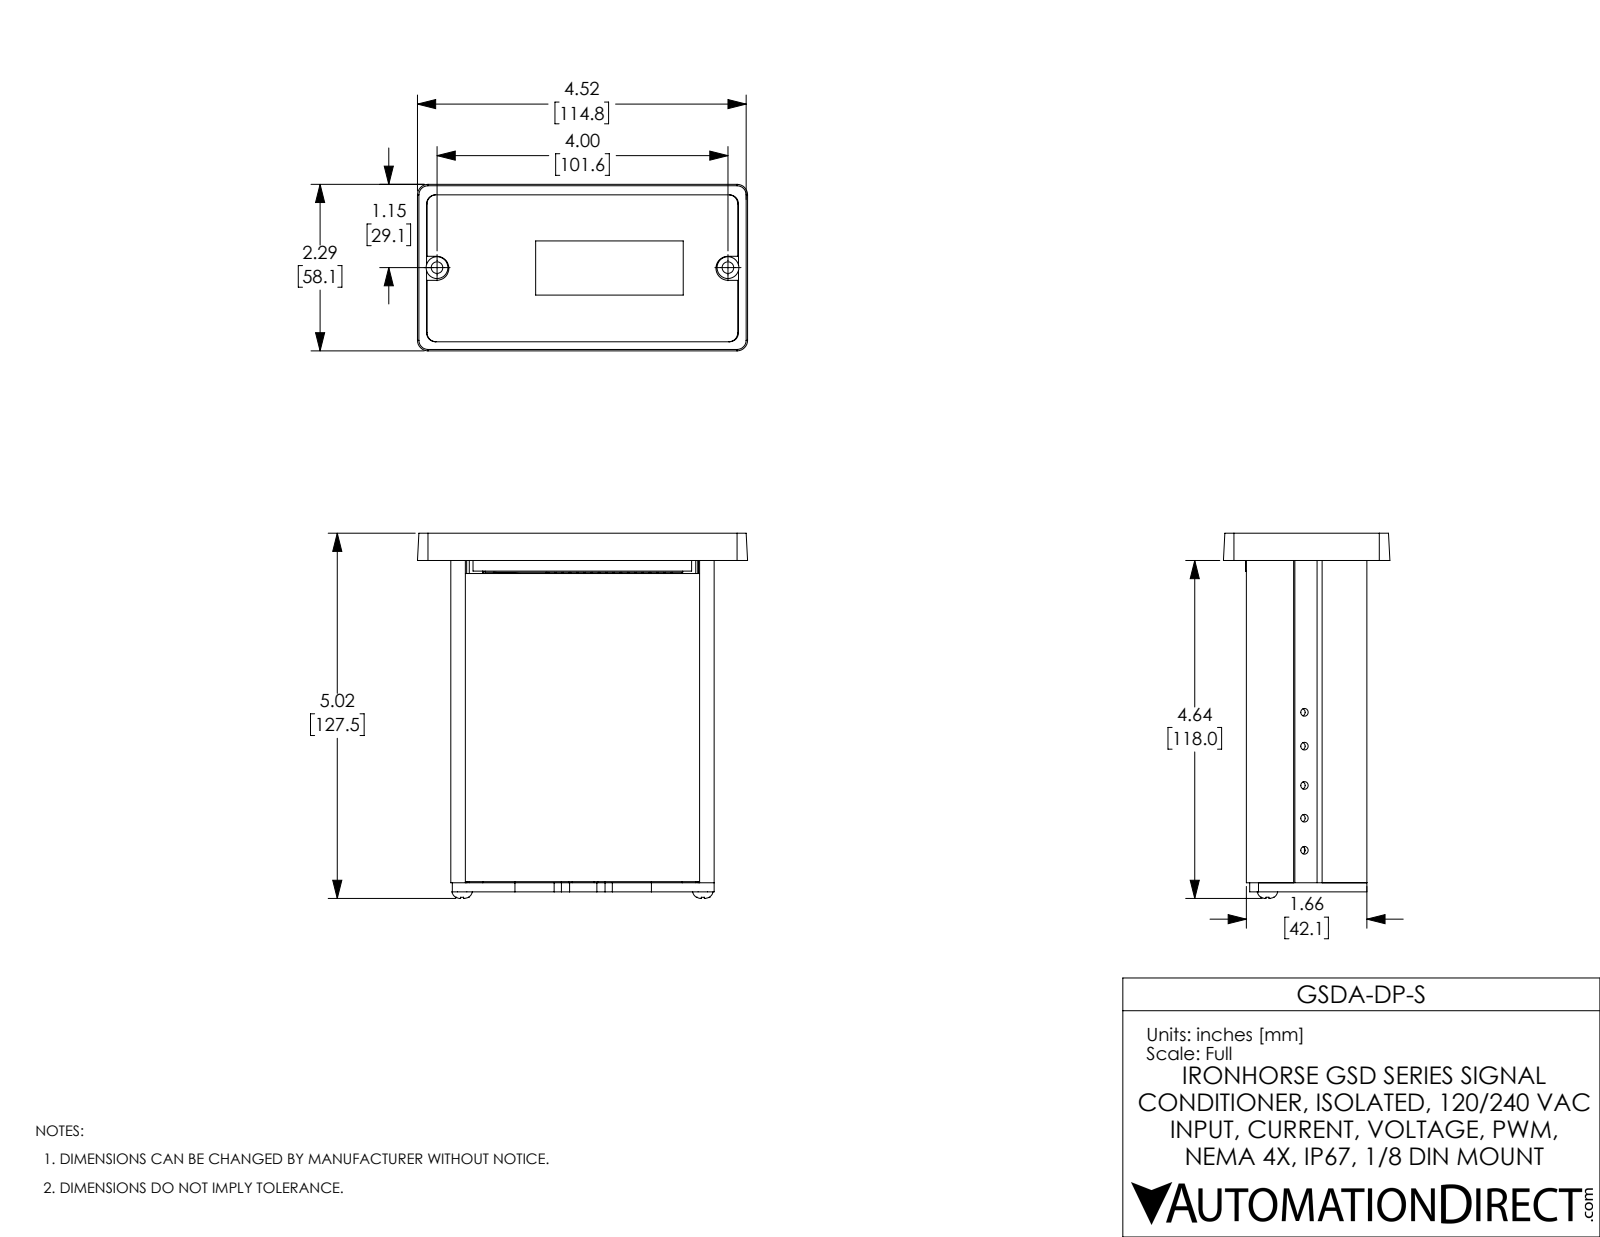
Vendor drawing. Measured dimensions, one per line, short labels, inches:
name: GSDA-DP-S
written by: SolidWorks 2017 (AUTOMOTIVE_DESIGN)
unit: in
bodies: 15 solids, 1227 faces (759 planar, 447 cylindrical, 21 other)
size: 5.019 × 4.539 × 2.289
volume: 9.053 in³; area: 219 in²
holes: 36× ⌀0.033, 13× ⌀0.035, 12× ⌀0.157, 6× ⌀0.02, 6× ⌀0.059, 6× ⌀0.147, 6× ⌀0.16, 5× ⌀0.106, 4× ⌀0.12, 4× ⌀0.285, 3× ⌀0.016, 3× ⌀0.112
bosses: 36× ⌀0.02, 3× ⌀0.247, 2× ⌀0.134
rounds: 18× R0.05, 16× R0.039, 12× R0.125, 10× R0.126, 7× R0.025, 4× R0.016, 4× R0.035, 4× R0.045
face distances: 0.1, 1.521, 0.045, 1.566, 1.421, 1.466, 0.031, 1.313, 0.209, 0.178
hole spacings: 0.197, 0.394, 0.591, 0.787, 0.984, 1.181, 0.1, 0.2
